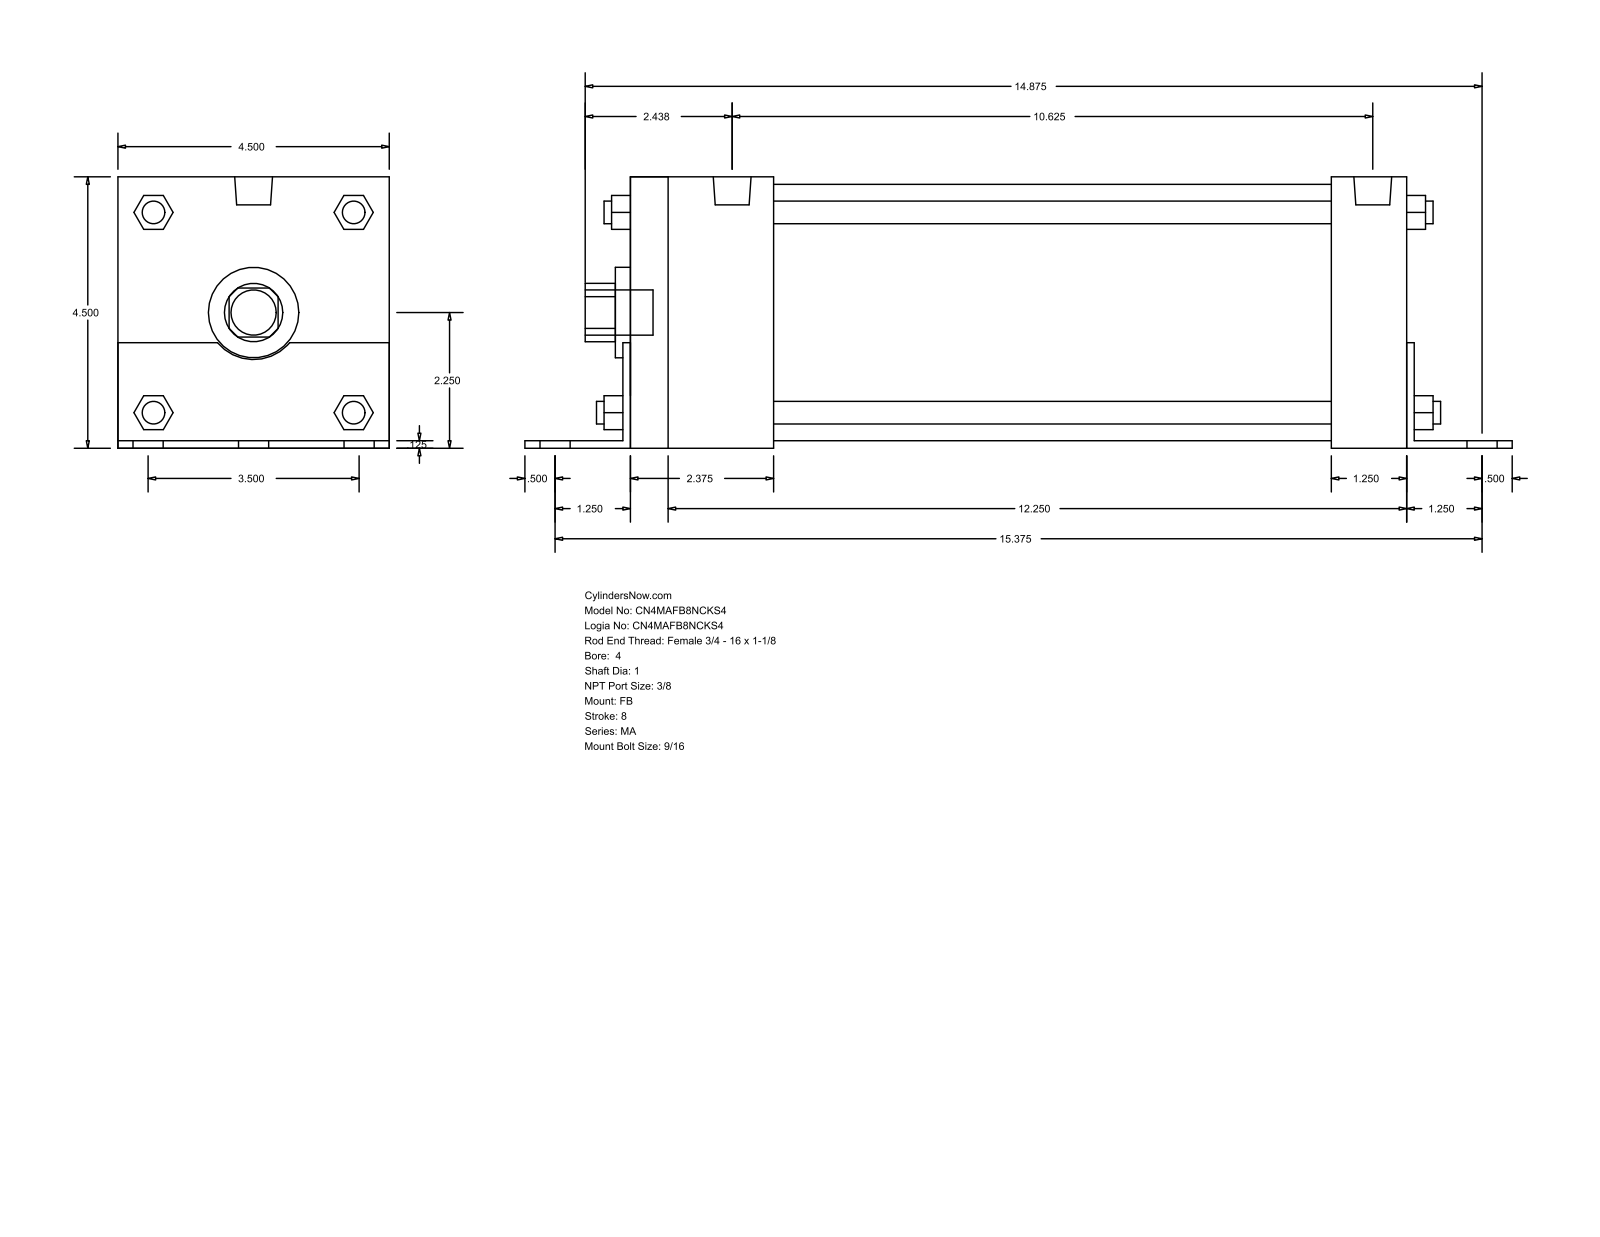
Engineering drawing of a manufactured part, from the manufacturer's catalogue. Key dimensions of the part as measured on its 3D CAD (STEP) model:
Part name (STEP PRODUCT): MA_FB__0400_1
STEP written by: GSSL Pune (CONFIG_CONTROL_DESIGN)
Units: millimetres
Bodies: 0 solids, 140 faces (105 planar, 35 cylindrical, 0 other)
Overall size (bounding box): 415.93 × 114.35 × 114.3
Round holes (diameter × count): ⌀25.4 ×1, ⌀38.1 ×1, ⌀107.95 ×1
Round bosses / shafts (diameter × count): ⌀14.29 ×6, ⌀11.11 ×4, ⌀9.53 ×4, ⌀15.93 ×2, ⌀19.05 ×1
Partial cylindrical surfaces — rounded edges, fillets, slot ends (radius × count): R12.29 ×1, R19.81 ×1
Main face-to-face distances: 114.3, 3.17, 114.35, 3.12, 111.18, 327.02, 3.18, 333.37, 330.2, 330.19
